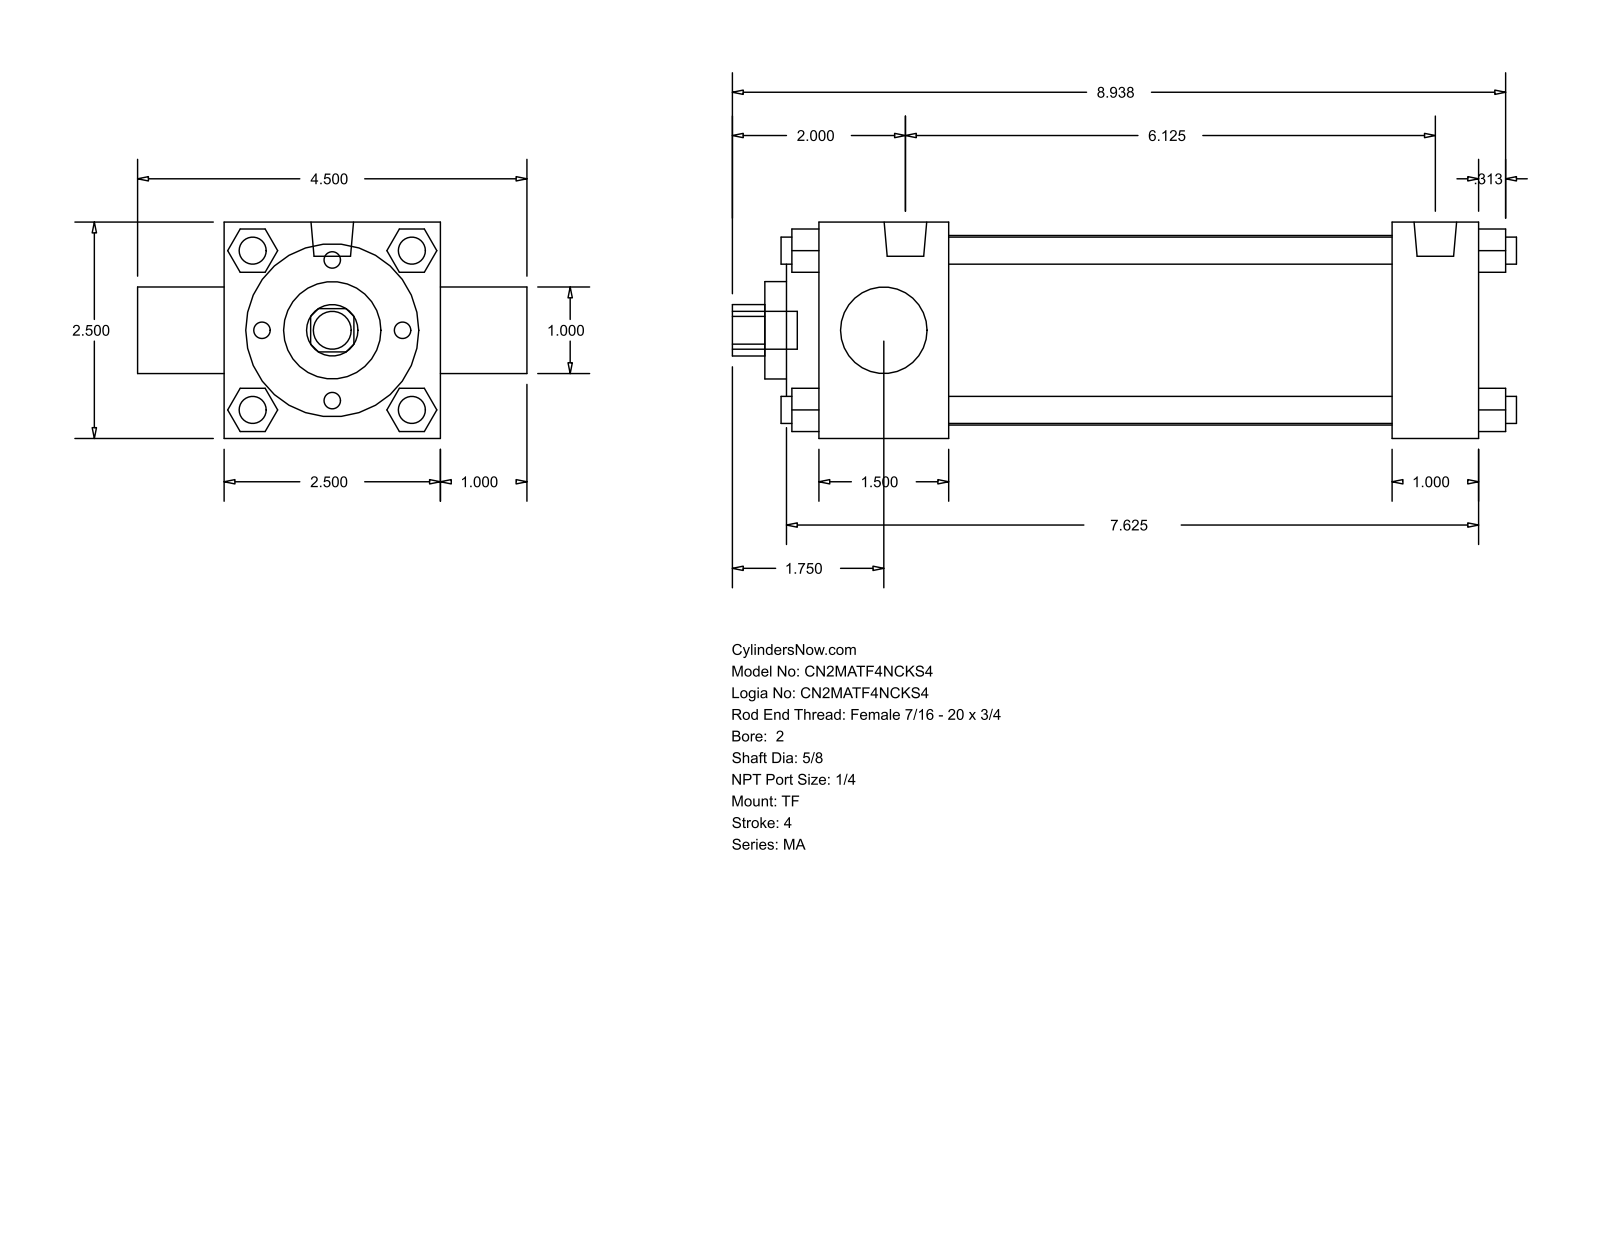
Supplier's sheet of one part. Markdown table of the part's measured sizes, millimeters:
| quantity | value |
| --- | --- |
| part name | MA_TF__0200_0.625 |
| STEP written by | GSSL Pune (CONFIG_CONTROL_DESIGN) |
| units | millimeters |
| bodies | 0 solids, 122 faces (93 planar, 29 cylindrical, 0 other) |
| overall size | 230.19 × 114.3 × 63.5 |
| round holes (diameter × count) | 15.88 × 1, 25.4 × 1, 28.57 × 1, 50.8 × 1, 55.63 × 1 |
| round bosses / shafts (diameter × count) | 7.94 × 7, 12.49 × 2, 11.11 × 1 |
| partial cylindrical surfaces (radius × count) | 7.54 × 1 |
| main face-to-face distances | 63.5, 38.1, 12.7, 9.52, 193.67, 168.28, 130.18, 155.57, 25.39, 47.62 |
